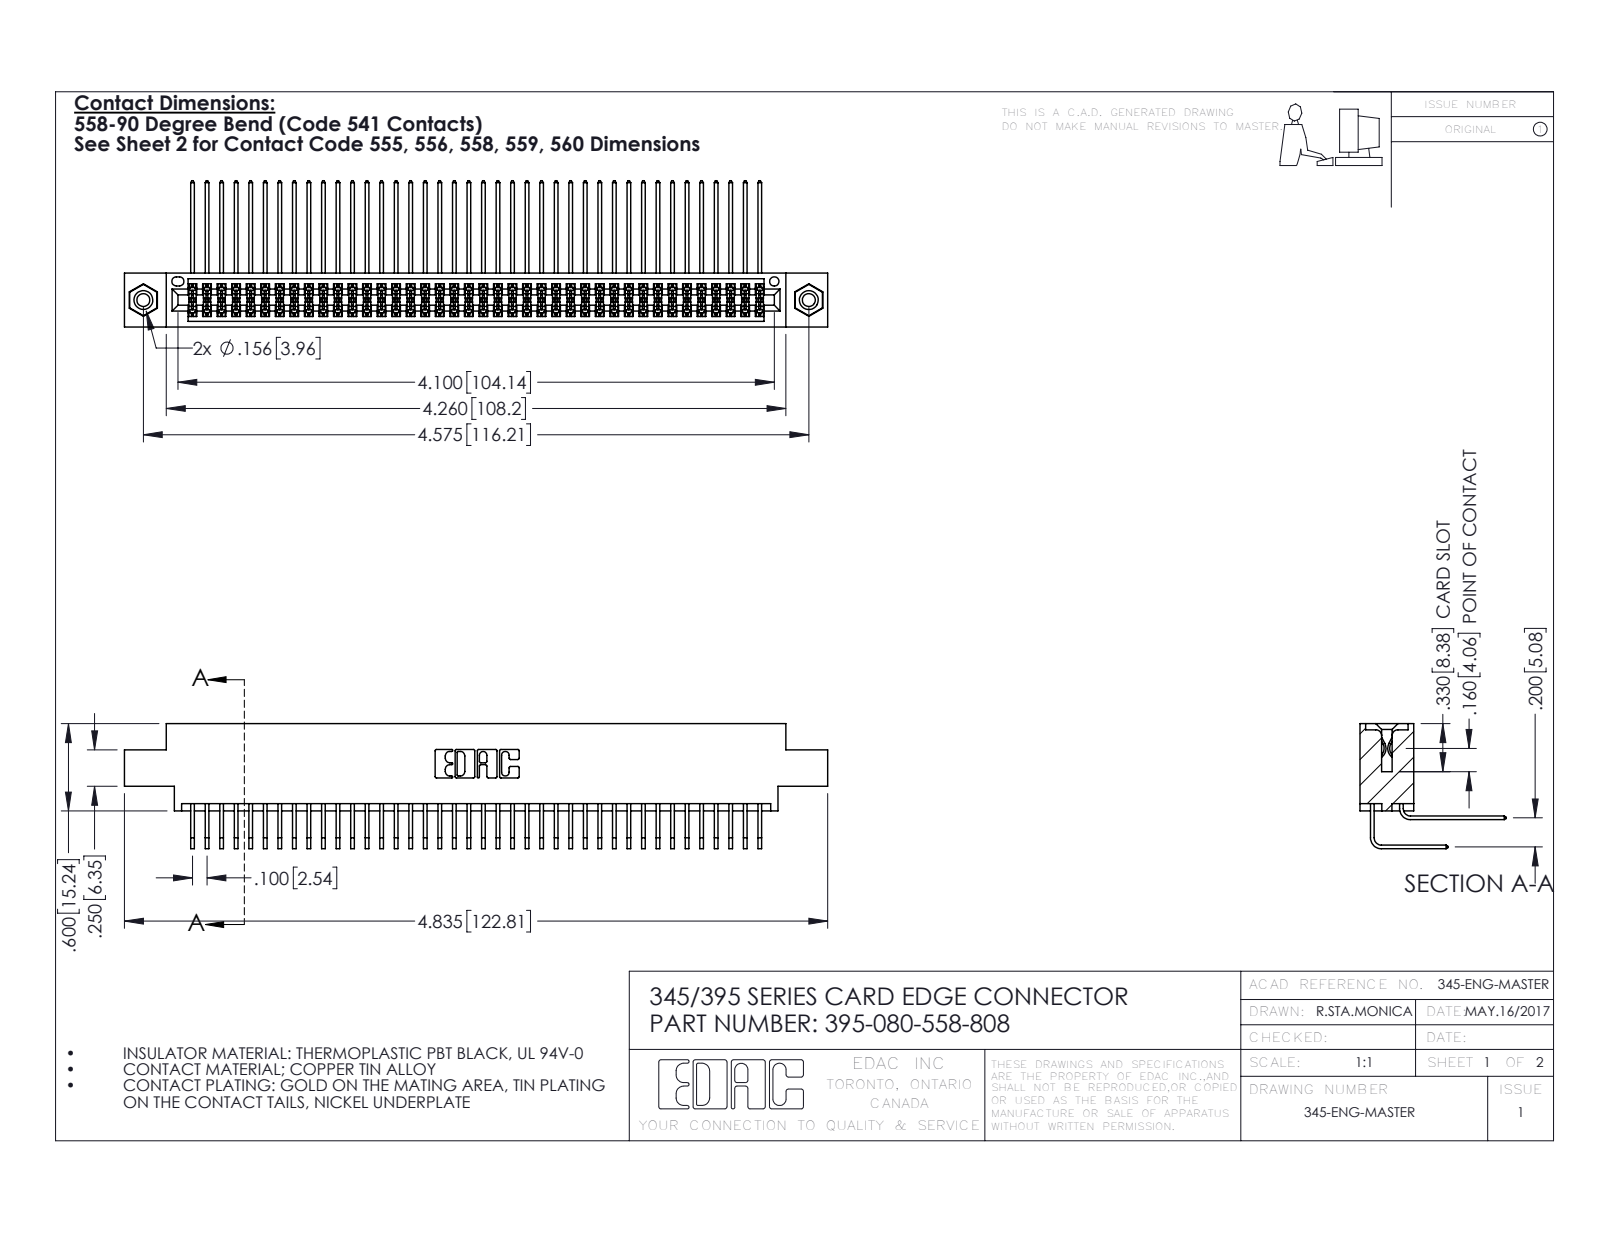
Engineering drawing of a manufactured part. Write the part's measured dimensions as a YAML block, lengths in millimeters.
part_name: "345-250-001_345-250-003-102; 345-292-001_558 559 Tail - 1; 345-292-001_558 Tail - 2; 345 Part_0.170 Offset - 0.156 Dia-TI (+1 more)"
step_written_by: "SolidWorks 2016 (CONFIG_CONTROL_DESIGN)"
units: millimeters
bodies: {solids: 83, faces: 4350, planar: 2916, cylindrical: 1418, other: 16}
overall_size: [122.8, 25.5, 21.8]
volume: 12300
surface_area: 20400
round_holes:
  - {diameter: 2.3, count: 2}
  - {diameter: 3.2, count: 2}
  - {diameter: 4, count: 2}
  - {diameter: 1.6, count: 1}
round_bosses_or_shafts:
  - {diameter: 3.9, count: 2}
partial_cylinders:
  - {radius: 0.2, count: 121}
  - {radius: 0.3, count: 22}
  - {radius: 0.2, count: 6}
  - {radius: 0.8, count: 6}
  - {radius: 0.7, count: 3}
  - {radius: 0.4, count: 2}
  - {radius: 0.5, count: 2}
  - {radius: 0.6, count: 2}
face_to_face_distances: [1.8, 7.6, 5.1, 9.4, 2.5, 6.9, 0.6, 5.7, 4.4, 0.6]
hole_center_spacings: [6.9, 110.2, 116.2]
